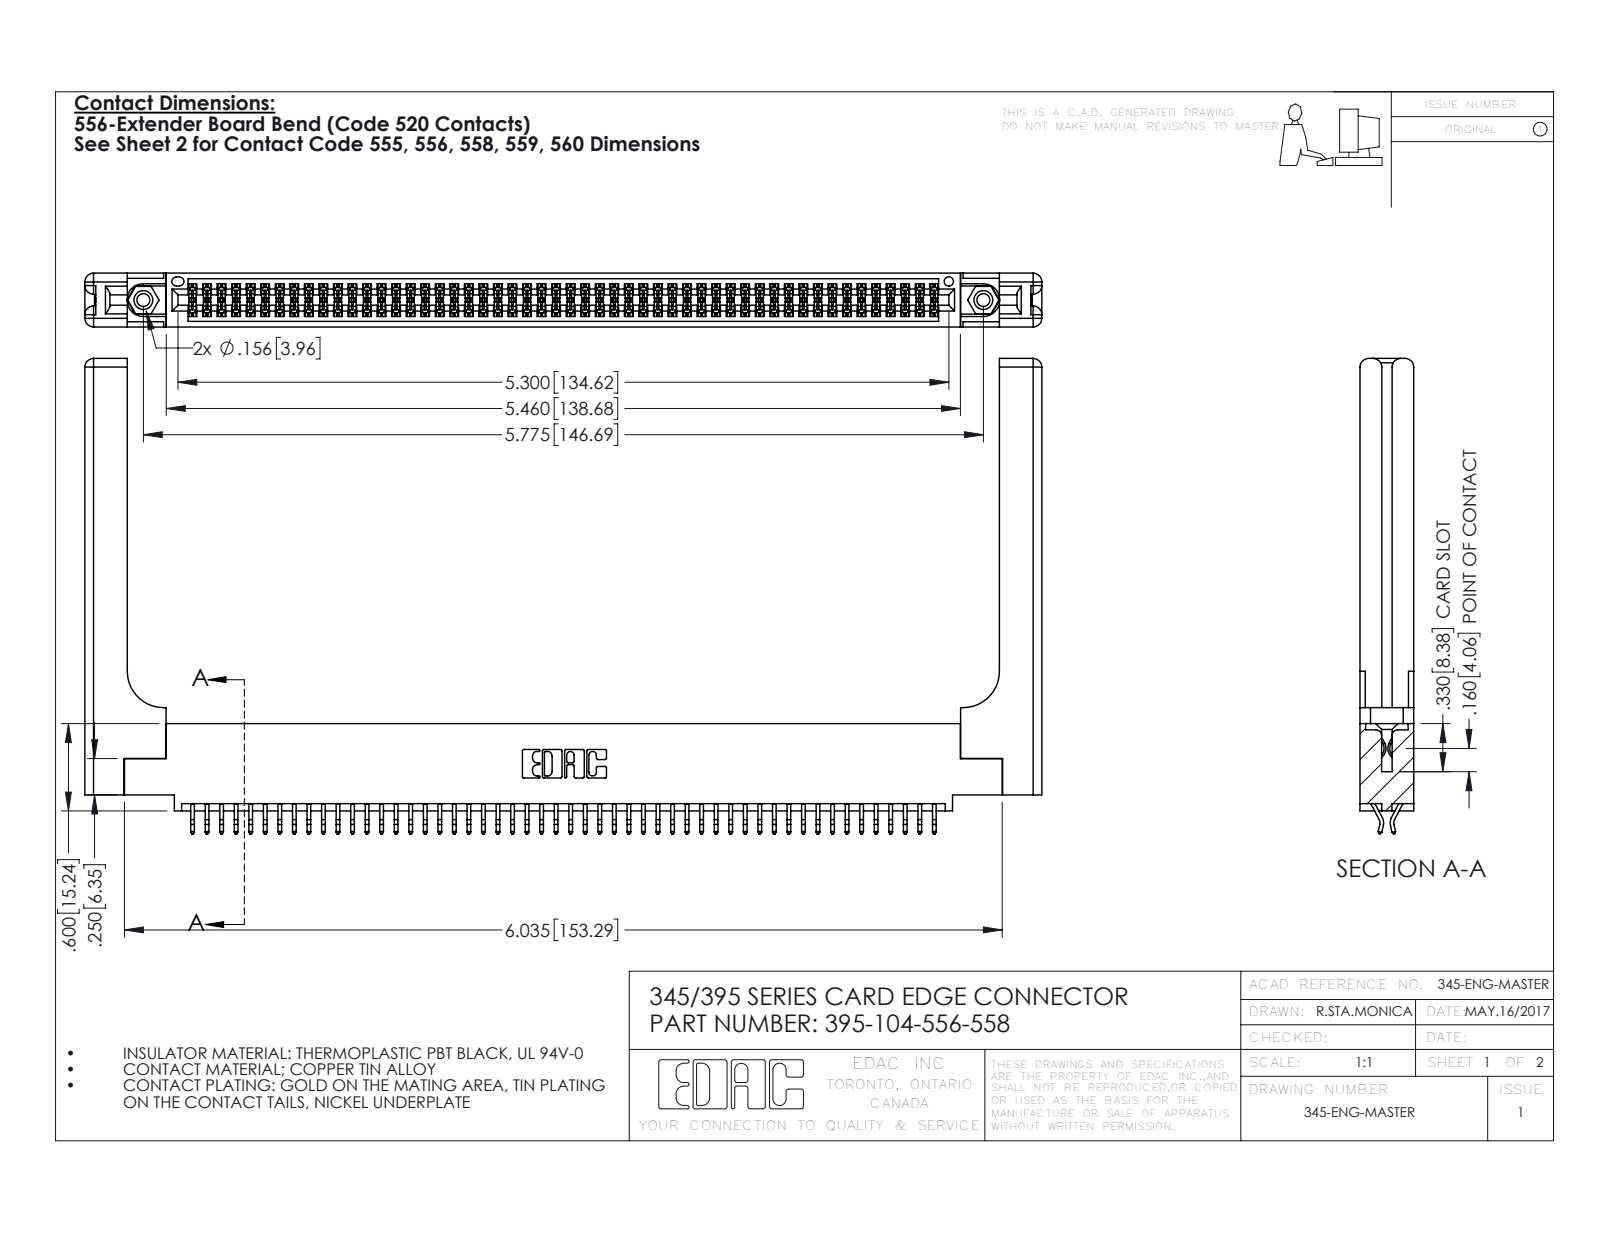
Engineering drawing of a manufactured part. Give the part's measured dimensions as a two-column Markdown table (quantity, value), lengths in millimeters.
| quantity | value |
| --- | --- |
| part name | 345-250-001_345-250-001-102; 345-292-001_556 Tail; 345 Part_0.110 Offset - 0.156 Dia-TH; 345-220-058_345-220-058 (+1 more) |
| STEP written by | SolidWorks 2016 (CONFIG_CONTROL_DESIGN) |
| units | millimeters |
| bodies | 109 solids, 6210 faces (4080 planar, 2070 cylindrical, 60 other) |
| overall size | 167.1 × 83 × 9.4 |
| volume | 24 730 mm³ |
| surface area | 29 270 mm² |
| round holes (diameter × count) | 2.3 × 2, 3.2 × 2, 4 × 2, 1.6 × 1 |
| round bosses / shafts (diameter × count) | 3.9 × 2 |
| partial cylindrical surfaces (radius × count) | 0.2 × 156, 0.3 × 22, 1.5 × 16, 0.2 × 6, 0.8 × 6, 0.7 × 3, 0.3 × 2, 0.4 × 2 |
| main face-to-face distances | 1.8, 7.6, 9.4, 0.6, 2.5, 6.9, 5.1, 5.7, 3.8, 3.8 |
| hole center spacings | 6.9, 140.7, 146.7 |
